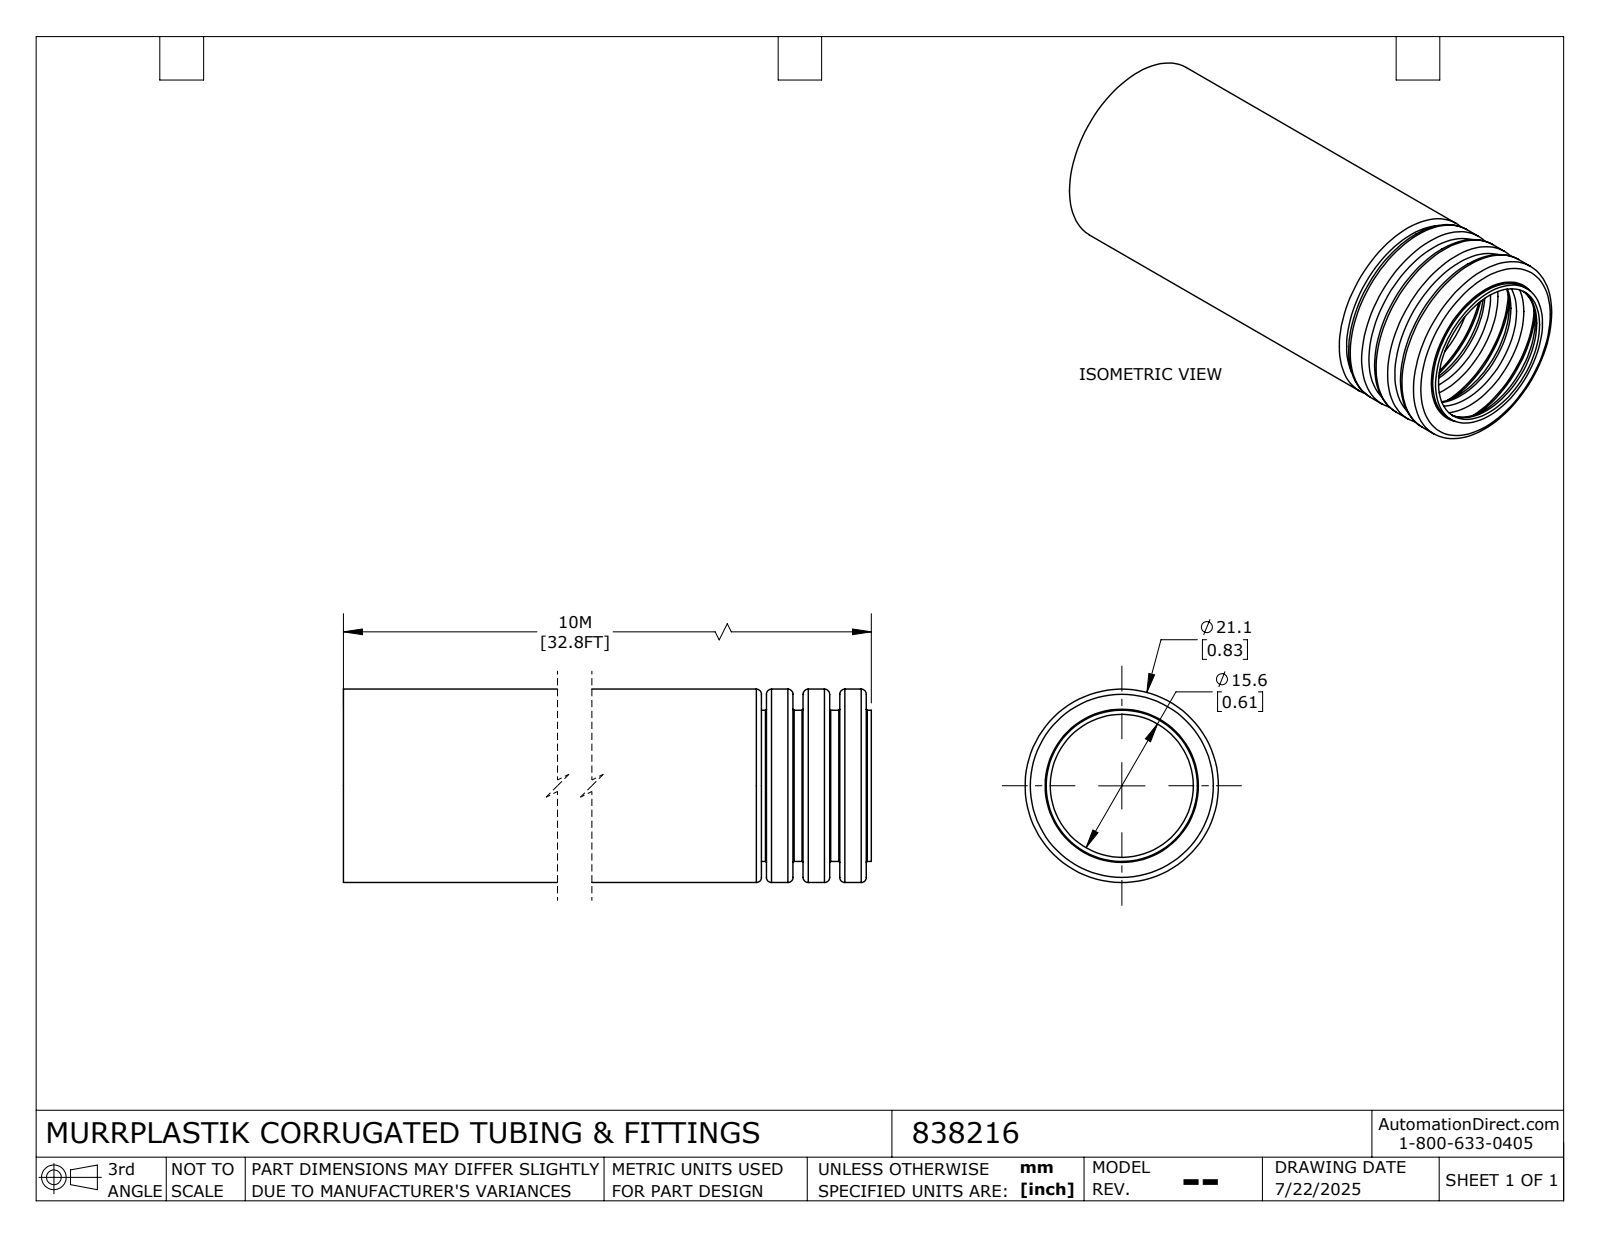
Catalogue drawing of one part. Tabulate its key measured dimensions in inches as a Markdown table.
| quantity | value |
| --- | --- |
| part name | 838216_Default |
| STEP written by | SolidWorks 2024 (CONFIG_CONTROL_DESIGN) |
| units | inches |
| bodies | 1 solid, 55 faces (15 planar, 15 cylindrical, 25 other) |
| overall size | 2.134 × 0.831 × 0.831 |
| volume | 0.447 in³ |
| surface area | 12.37 in² |
| round holes (diameter × count) | 0.614 × 1, 0.795 × 1 |
| round bosses / shafts (diameter × count) | 0.831 × 1, 0.65 × 1 |
| main face-to-face distances | 0.157, 0.096, 0.018, 0.079, 0.254, 0.315, 0.061, 0.175, 0.14, 0.114 |
